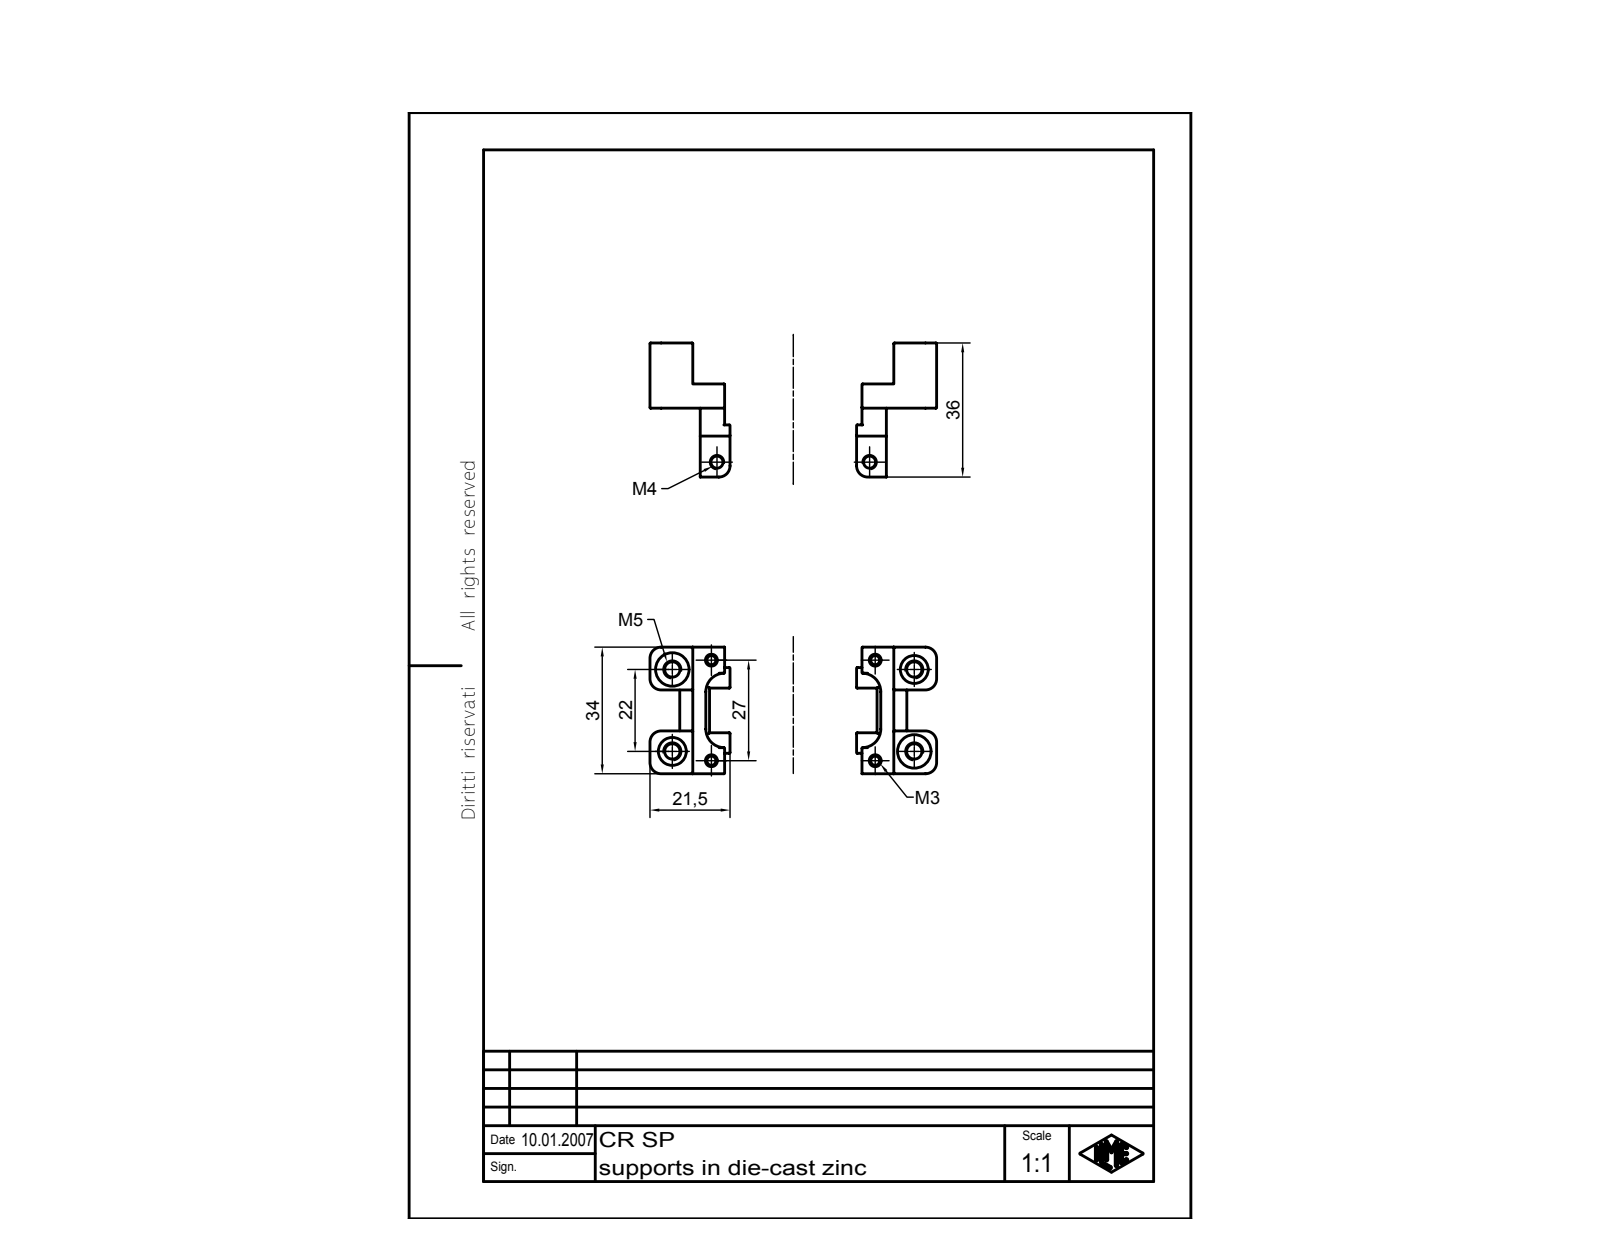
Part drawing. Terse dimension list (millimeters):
name: CR SP
written by: Autodesk Inventor 7 (AUTOMOTIVE_DESIGN)
unit: mm
bodies: 2 solids, 496 faces (148 planar, 246 cylindrical, 102 other)
size: 77 × 36 × 34
volume: 12 390 mm³; area: 9 513 mm²
holes: 4× ⌀7.5, 2× ⌀3.24, 1× ⌀0.21
rounds: 60× R0.2, 20× R0.1, 10× R3, 5× R5
face distances: 11.5, 8, 11, 5.5, 2, 2.5, 52, 3.5, 13.5, 4.5
hole spacings: 22, 65, 68.62, 41
